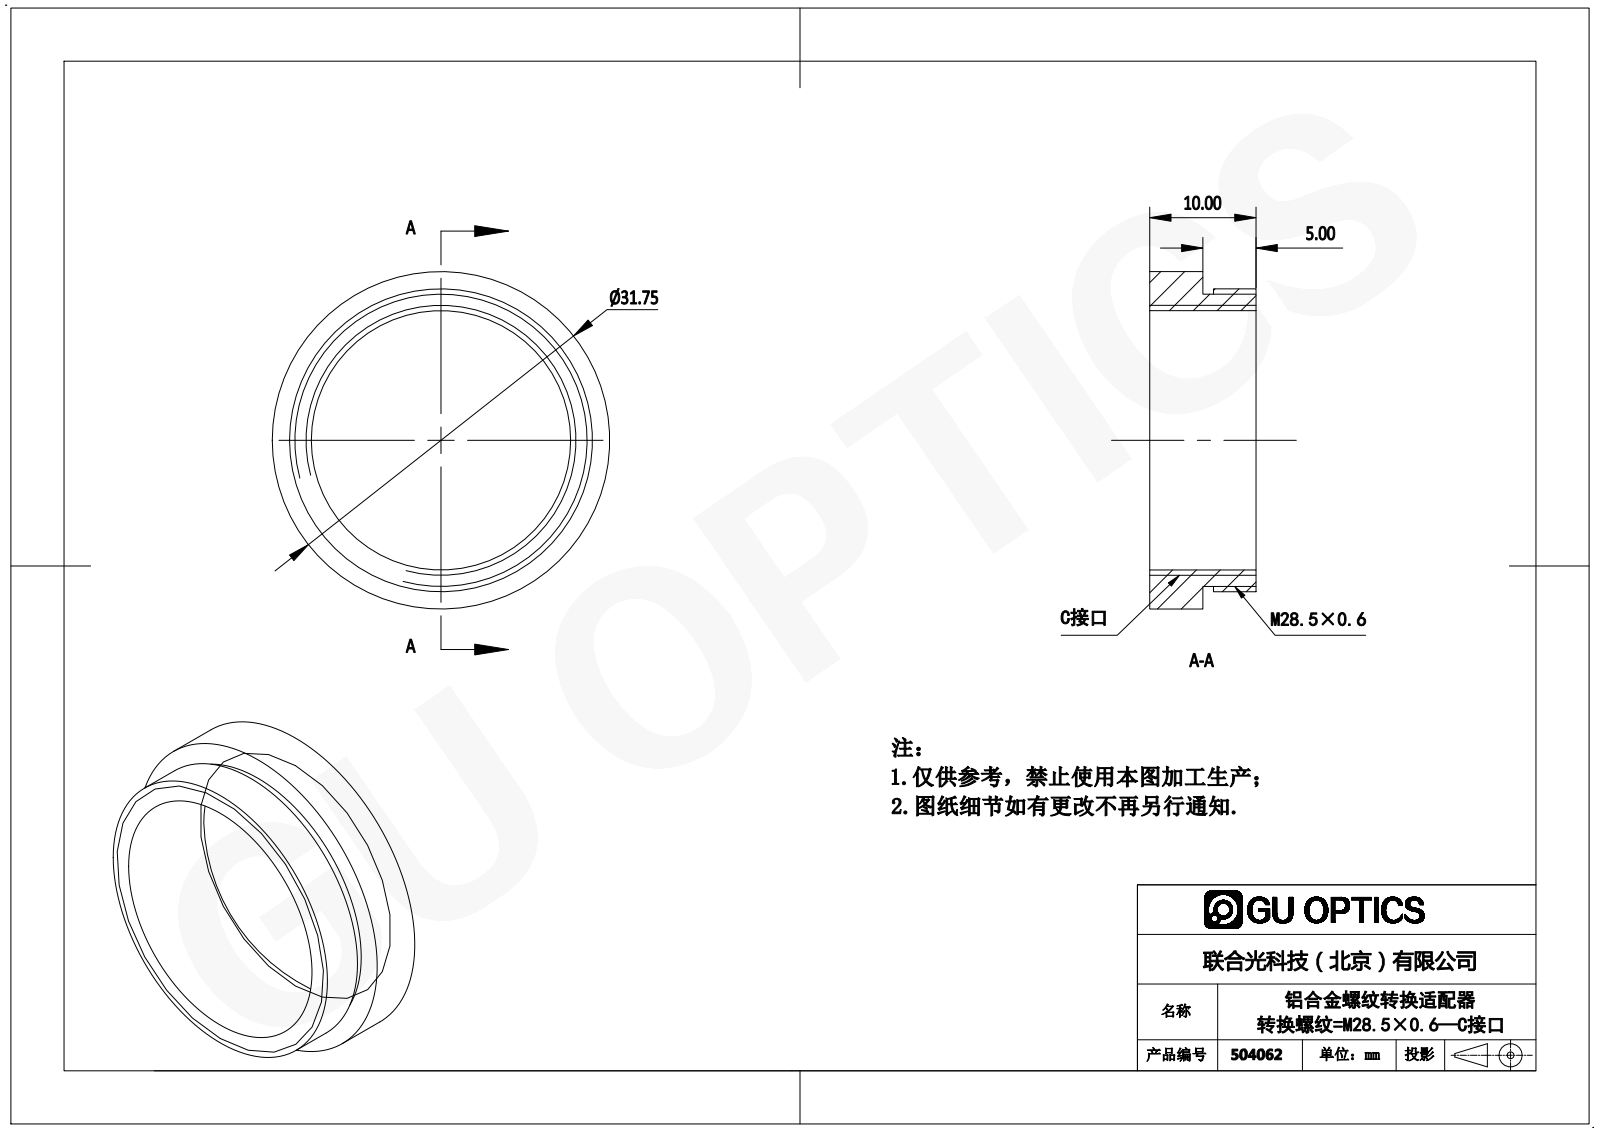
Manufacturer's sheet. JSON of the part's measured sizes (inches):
{"part_name": "504062", "step_written_by": "SolidWorks 2016 (AUTOMOTIVE_DESIGN)", "units": "inches", "bodies": {"solids": 1, "faces": 12, "planar": 4, "cylindrical": 8, "other": 0}, "overall_size": [1.25, 1.25, 0.394], "volume_in3": 0.148, "surface_area_in2": 3.791, "round_holes": [[0.961, 1]], "round_bosses_or_shafts": [[1.25, 1], [1.122, 1], [1.083, 1]], "face_to_face_distances": [0.197, 0.394, 0.236, 0.039, 0.157]}
